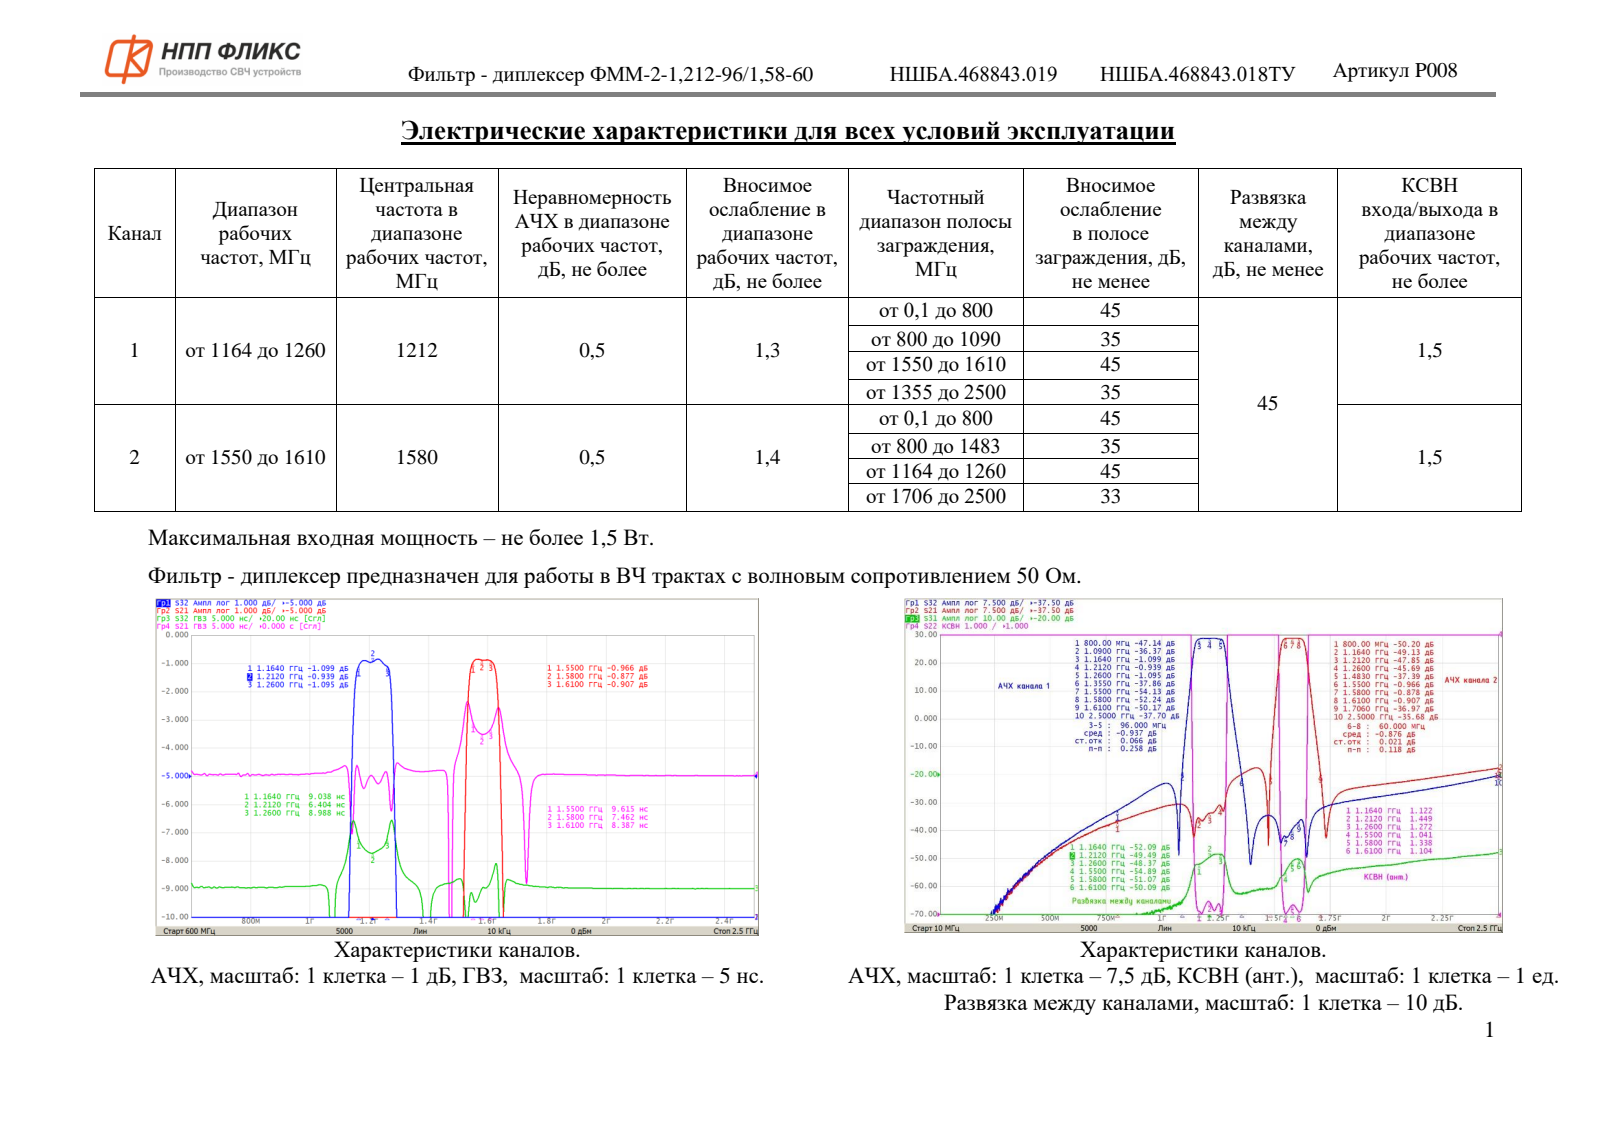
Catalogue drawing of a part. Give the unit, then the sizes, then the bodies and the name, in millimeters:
Units: millimetres
Overall size (bounding box): 18 × 9.85 × 4.3
Partial cylindrical surfaces — rounded edges, fillets, slot ends (radius × count): R0.5 ×23, R0.24 ×3, R0.12 ×1, R0.3 ×1, R0.36 ×1, R0.42 ×1, R0.6 ×1
Main face-to-face distances: 4.3, 1.79, 1.49, 1.91, 7.94, 9.85, 7.64, 9.55, 6.15, 8.06
Volume: 568 mm³ · Surface area: 651 mm²
Bodies: 1 solid, 965 faces (806 planar, 38 cylindrical, 121 other)
Part name (STEP PRODUCT): НШБА.468843.019_Диплексер ФММ-2-1,212-96(1,58-60
STEP written by: ASCON Math Kernel (CONFIG_CONTROL_DESIGN)
